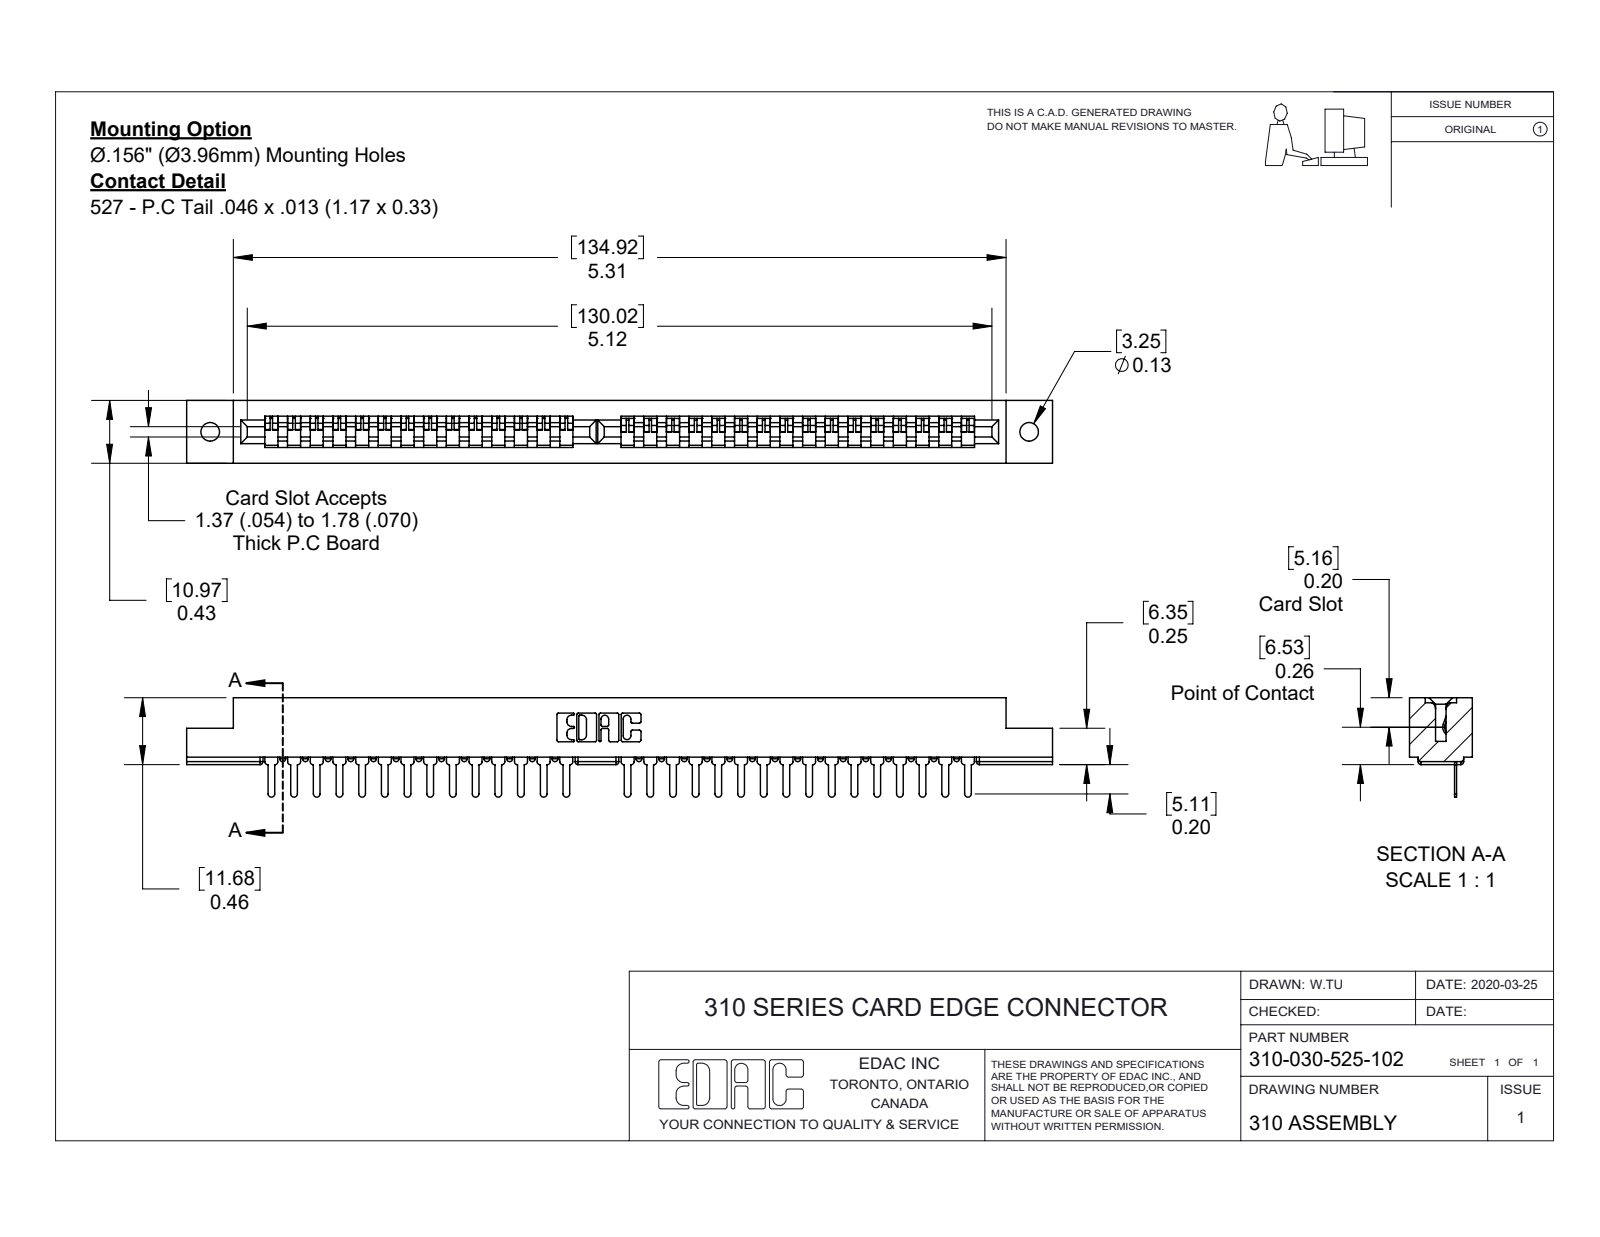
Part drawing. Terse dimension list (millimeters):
name: 307-290-001_525; 310-030-525-102; 310 Part_.128 Dia. Hole
written by: SolidWorks 2016 (CONFIG_CONTROL_DESIGN)
unit: mm
bodies: 31 solids, 1846 faces (1194 planar, 588 cylindrical, 64 other)
size: 151.21 × 17.37 × 10.97
volume: 12 609 mm³; area: 14 522 mm²
holes: 2× ⌀3.25
rounds: 158× R0.51, 30× R0.58, 22× R0.25, 6× R0.17, 6× R0.8, 3× R0.67, 2× R0.3, 2× R0.64
face distances: 2.76, 8.22, 10.98, 0.38, 1.82, 0.33, 10.38, 5.46, 4.58, 6.4
hole spacings: 143
